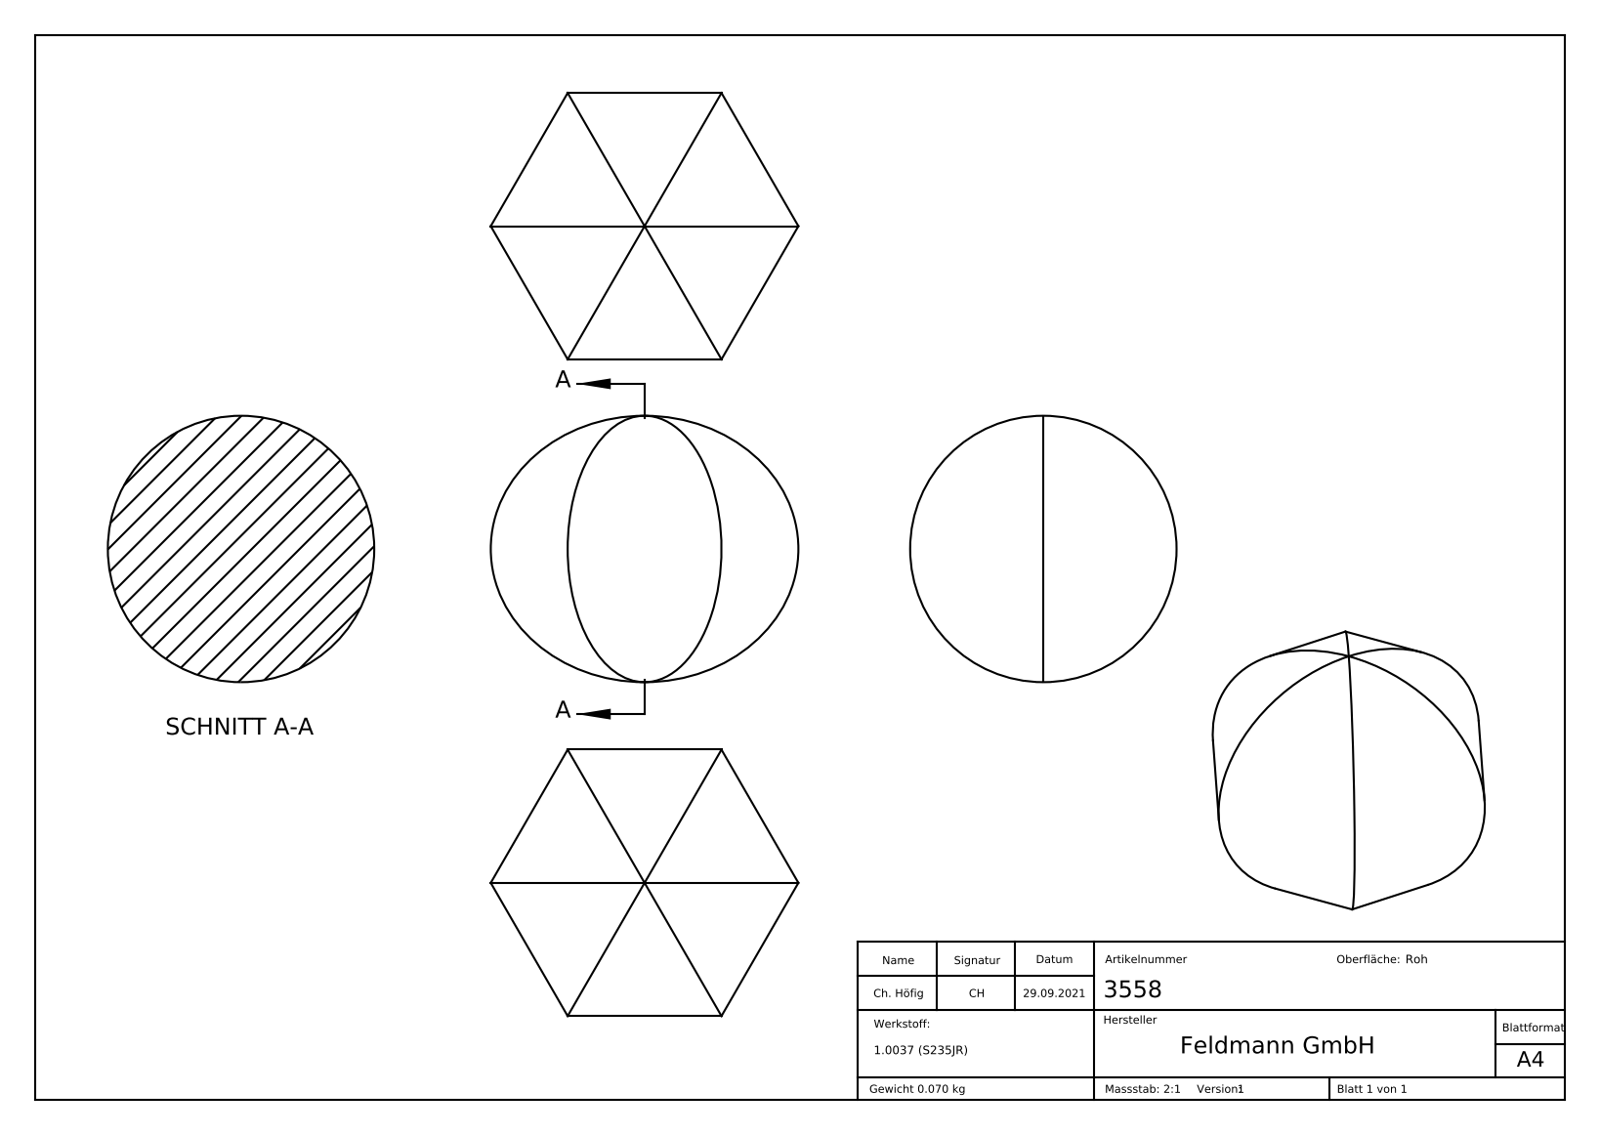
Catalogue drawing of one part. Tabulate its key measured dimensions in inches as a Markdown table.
| quantity | value |
| --- | --- |
| part name | 3558 |
| STEP written by | SolidWorks 2018 (CONFIG_CONTROL_DESIGN) |
| units | inches |
| bodies | 1 solid, 6 faces (0 planar, 6 cylindrical, 0 other) |
| overall size | 1.137 × 0.984 × 0.984 |
| volume | 0.55 in³ |
| surface area | 3.356 in² |
| round bosses / shafts (diameter × count) | 0.984 × 3 |
